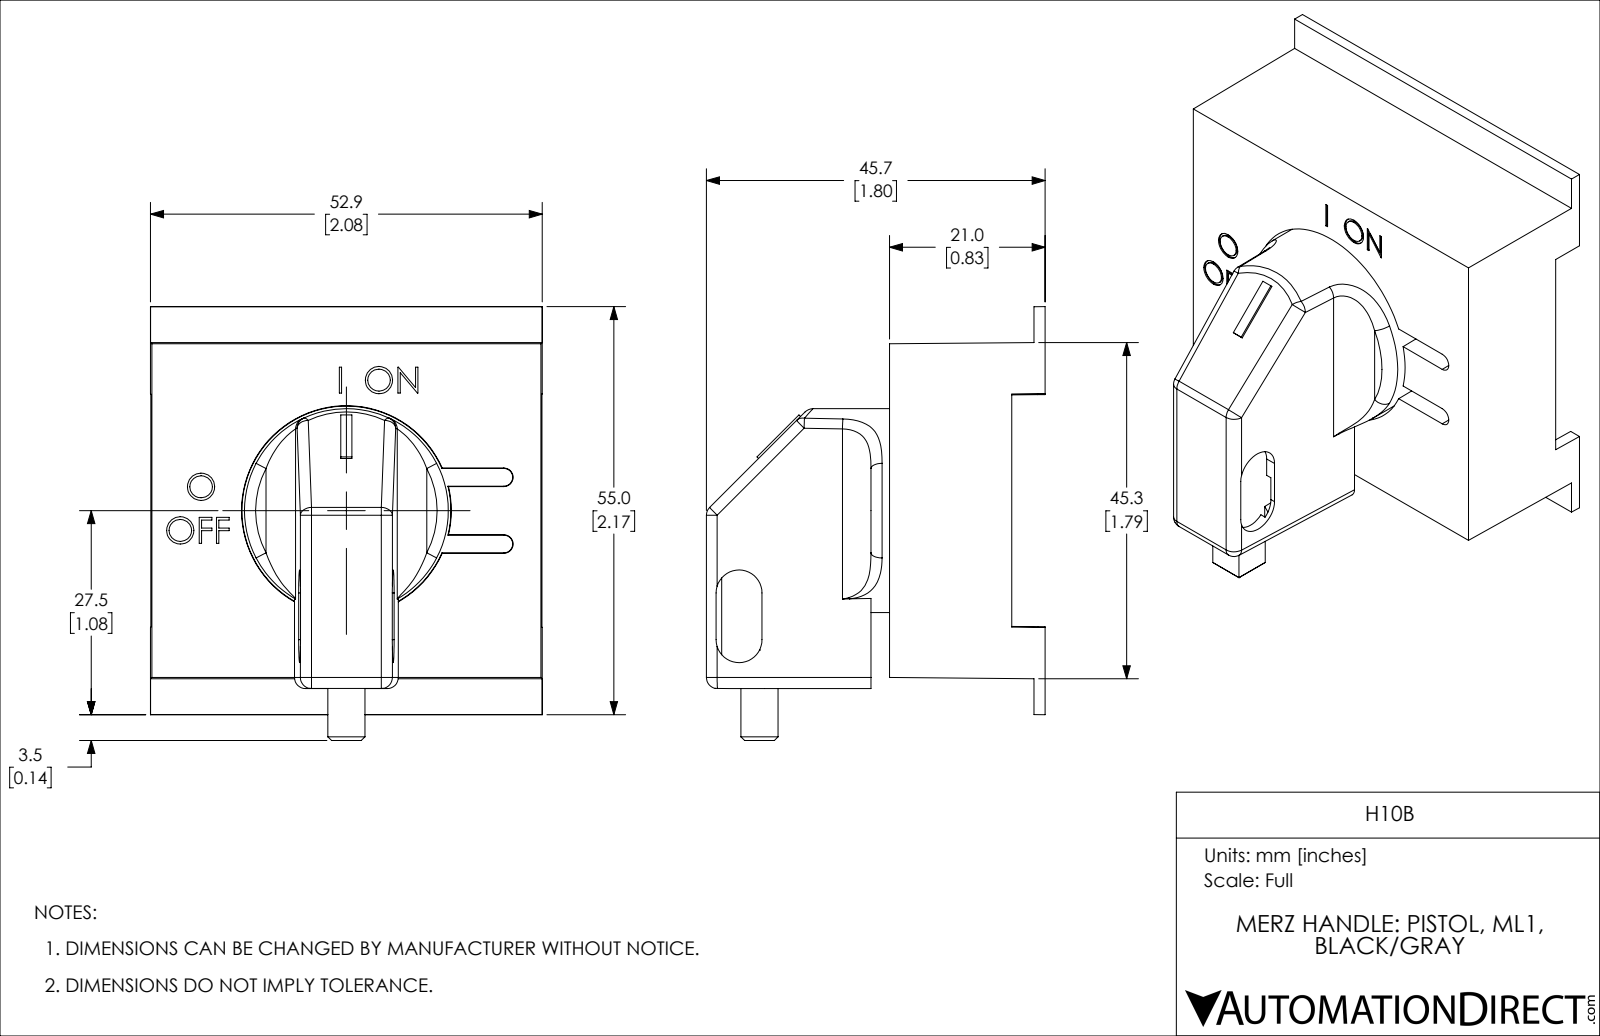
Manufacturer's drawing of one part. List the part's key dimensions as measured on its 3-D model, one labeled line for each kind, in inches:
Part name (STEP PRODUCT): H10B
STEP written by: SolidWorks 2019 (AUTOMOTIVE_DESIGN)
Units: inches
Bodies: 1 solid, 339 faces (225 planar, 42 cylindrical, 72 other)
Overall size (bounding box): 2.304 × 2.081 × 1.799
Volume: 1.535 in³ · Surface area: 32.45 in²
Round bosses / shafts (diameter × count): ⌀1.083 ×1, ⌀0.906 ×1
Partial cylindrical surfaces — rounded edges, fillets, slot ends (radius × count): R0.012 ×8, R0.059 ×8, R0.039 ×4, R0.02 ×3, R0.122 ×2, R0.157 ×2
Main face-to-face distances: 0.047, 0.094, 0.067, 0.059, 0.827, 0.531, 0.732, 0.492, 0.039, 0.419
